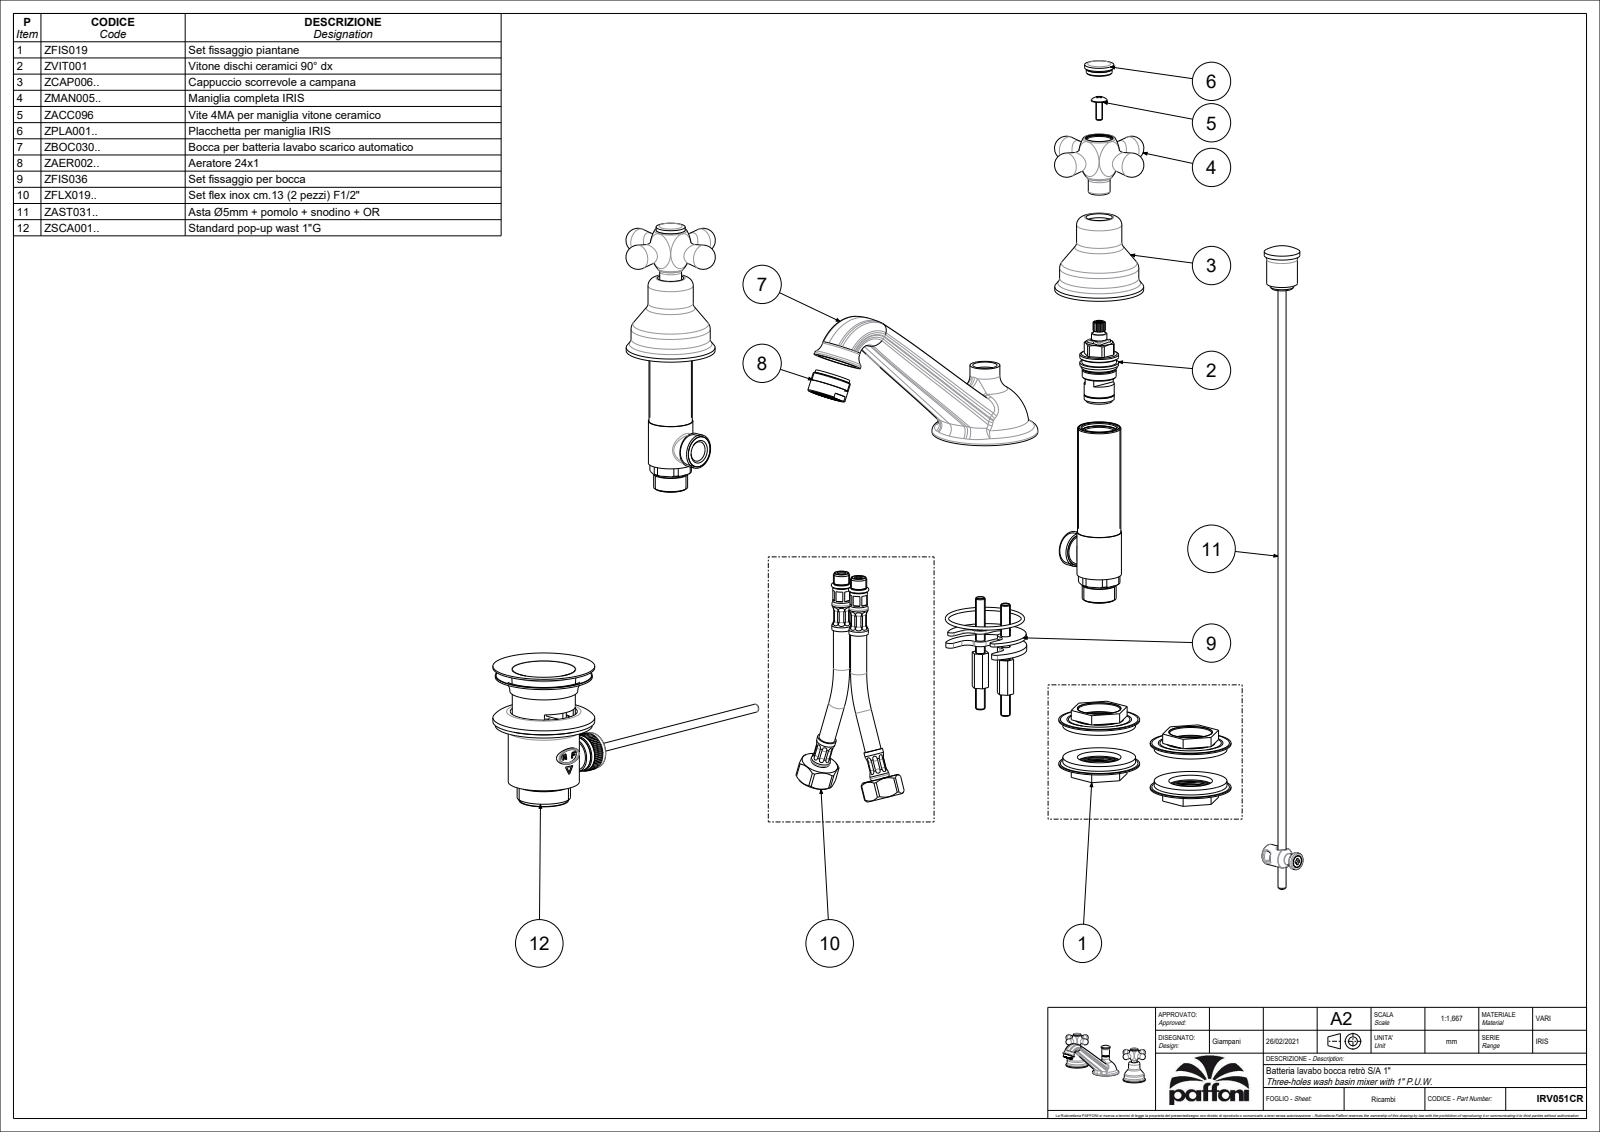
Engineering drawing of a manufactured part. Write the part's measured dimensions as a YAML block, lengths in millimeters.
part_name: "IRV051CR"
step_written_by: "CREO PARAMETRIC BY PTC INC, 2020044 (CONFIG_CONTROL_DESIGN)"
units: millimeters
bodies: {solids: 6, faces: 511, planar: 118, cylindrical: 82, other: 311}
overall_size: [272, 179.22, 94.3]
volume: 227551
surface_area: 78568
round_holes:
  - {diameter: 11, count: 3}
  - {diameter: 15, count: 3}
  - {diameter: 8, count: 2}
  - {diameter: 16.2, count: 2}
  - {diameter: 25.7, count: 2}
  - {diameter: 45, count: 2}
  - {diameter: 52.8, count: 2}
  - {diameter: 4.2, count: 1}
  - {diameter: 5.5, count: 1}
round_bosses_or_shafts:
  - {diameter: 55, count: 2}
  - {diameter: 49, count: 2}
  - {diameter: 29.5, count: 2}
  - {diameter: 28, count: 2}
  - {diameter: 24, count: 2}
  - {diameter: 18, count: 2}
  - {diameter: 13.5, count: 2}
  - {diameter: 65.5, count: 1}
face_to_face_distances: [44, 43.9, 15.9, 4, 12, 16, 28, 5.68, 61.5, 11.9]
hole_center_spacings: [100, 200]
